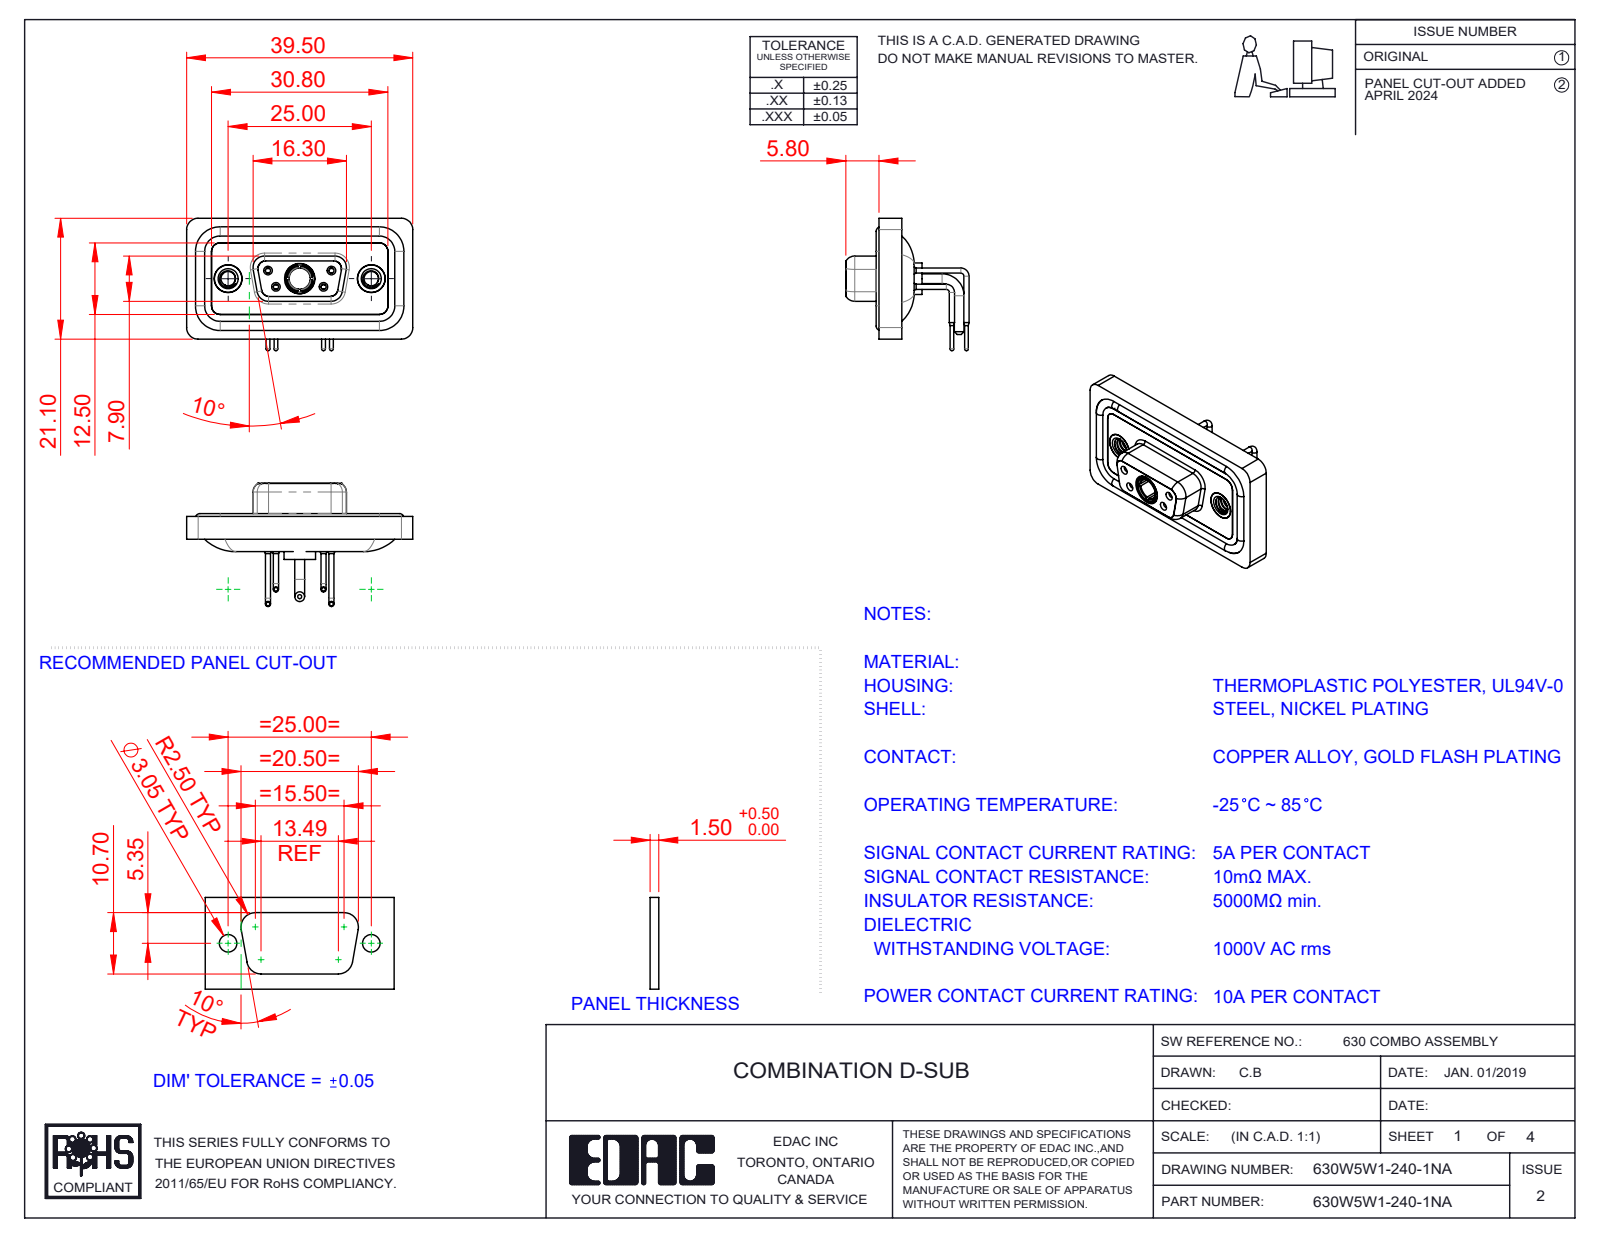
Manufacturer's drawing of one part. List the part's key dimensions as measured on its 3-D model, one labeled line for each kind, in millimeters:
Part name (STEP PRODUCT): 630W5W1-240-1NA; 630Combo Threaded Rivet_A; 630Combo Shell Rear_09 Contacts; 630Combo Contact Row 1_50 Contacts (+5 more)
STEP written by: SolidWorks 2023 (CONFIG_CONTROL_DESIGN)
Units: millimetres
Bodies: 13 solids, 670 faces (194 planar, 303 cylindrical, 173 other)
Overall size (bounding box): 39.5 × 23.12 × 21.53
Volume: 4 764 mm³ · Surface area: 7 796 mm²
Round holes (diameter × count): ⌀0.9 ×4, ⌀1.1 ×4, ⌀1.5 ×4, ⌀2 ×4, ⌀4.85 ×3, ⌀1.6 ×2, ⌀1.7 ×2, ⌀2.5 ×2, ⌀4 ×2, ⌀4.05 ×2, ⌀5 ×2, ⌀3.7 ×1
Round bosses / shafts (diameter × count): ⌀1.6 ×6, ⌀0.9 ×4, ⌀0.65 ×4, ⌀4.95 ×2, ⌀4.8 ×2, ⌀1.7 ×2, ⌀5.5 ×1, ⌀5.2 ×1
Partial cylindrical surfaces — rounded edges, fillets, slot ends (radius × count): R1.5 ×18, R2 ×18, R1.35 ×8, R1.6 ×8, R0.25 ×4, R0.5 ×4, R0.6 ×4, R0.65 ×4
Main face-to-face distances: 0.4, 1.8, 1.1, 2.9, 2.5, 1.6, 3.1, 1.5, 2.1, 0.5
Hole centre spacings: 3.16, 5.72, 7.1, 12.5, 18.1, 4.39, 4.4, 8.31
